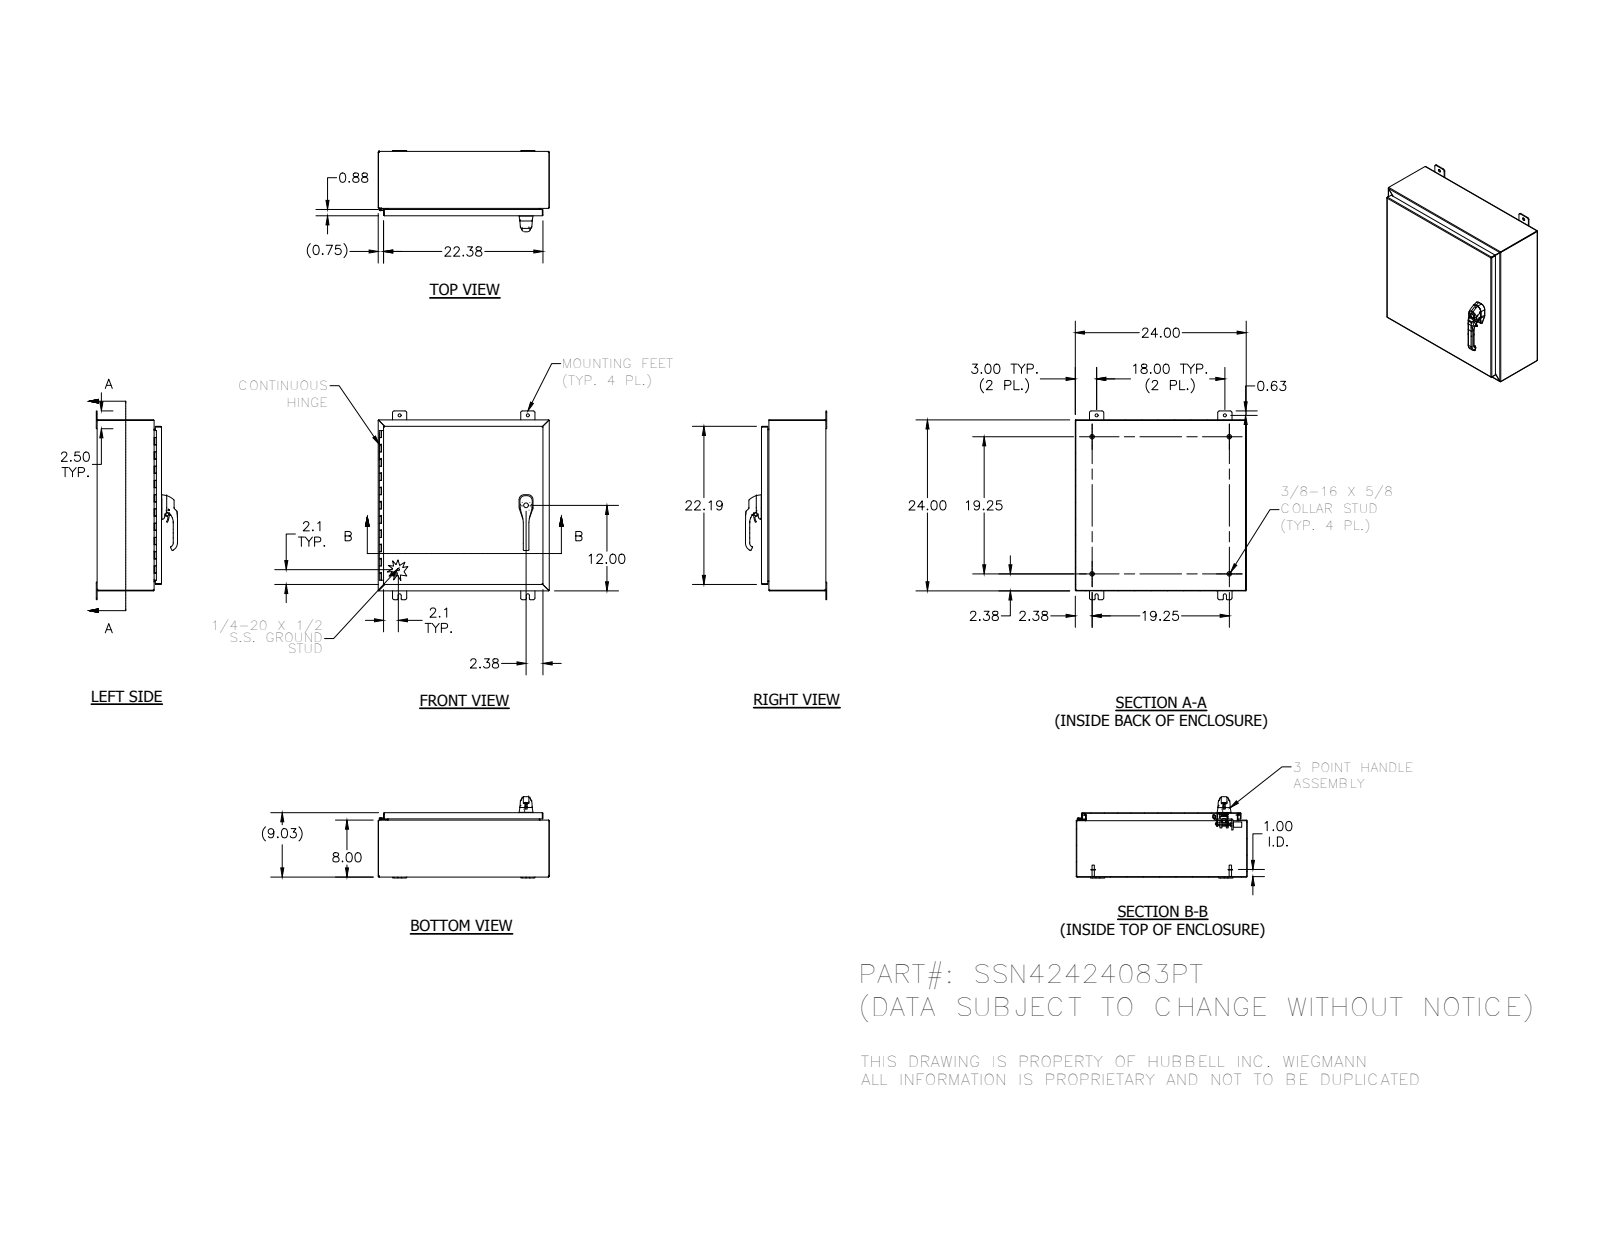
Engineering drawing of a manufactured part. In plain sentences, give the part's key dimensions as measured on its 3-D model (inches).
The part is named "328138T; 1091-BR11_AF0; SPACER; 1091-73 (+8 more)". Its 3-D file was written by "SolidWorks 2014 (AUTOMOTIVE_DESIGN)". It is 56 solids with 3059 faces: 1014 planar, 1260 cylindrical and 785 other. Overall it measures 26.5 by 24 by 11.408 inches. Its volume is 184.2 cubic inches and its surface area 4 728 square inches. Round holes: 8 of diameter 0.262, 4 of diameter 0.187, 4 of diameter 0.438, 3 of diameter 0.213, 3 of diameter 0.281, 2 of diameter 0.241, 2 of diameter 0.25, 2 of diameter 0.252, 2 of diameter 0.315, 2 of diameter 0.4, 2 of diameter 0.402, 2 of diameter 0.413. Round bosses or shafts: 4 of diameter 0.625, 4 of diameter 0.33, 3 of diameter 0.236, 2 of diameter 1, 2 of diameter 0.563, 2 of diameter 0.533, 2 of diameter 0.531, 2 of diameter 0.5. Partial cylindrical surfaces (rounded edges, fillets, slot ends): 172 of radius 0.02, 113 of radius 0.012, 26 of radius 0.125, 24 of radius 0.031, 21 of radius 0.019, 20 of radius 0.105, 20 of radius 0.25, 16 of radius 0.025. The main face-to-face distances are 0.074, 8.959, 23.926, 8.885, 9.033, 23.852, 24, 7.926, 1.033, 8. The hole center spacings are 0.38, 0.492, 0.76, 0.886, 14.428, 0.234, 0.258, 0.38.
